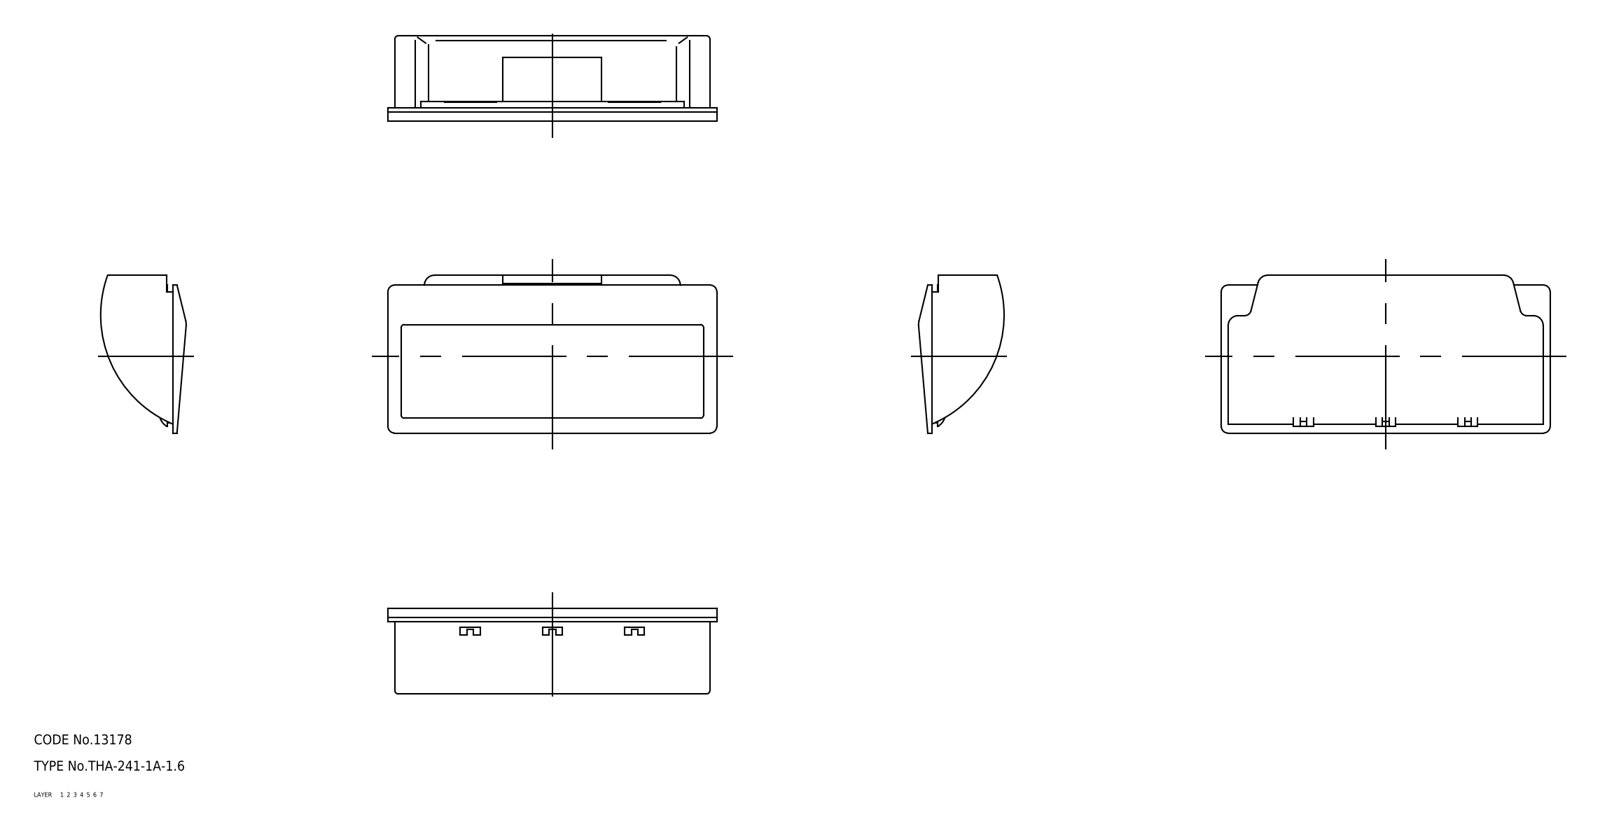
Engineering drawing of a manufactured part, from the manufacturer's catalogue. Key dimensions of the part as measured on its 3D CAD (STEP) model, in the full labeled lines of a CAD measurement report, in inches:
Part name (STEP PRODUCT): pull
STEP written by: CADfix (AUTOMOTIVE_DESIGN)
Units: inches
Bodies: 1 solid, 116 faces (0 planar, 0 cylindrical, 116 other)
Overall size (bounding box): 3.937 × 1.89 × 1.024
Volume: 1.478 in³ · Surface area: 30.76 in²
